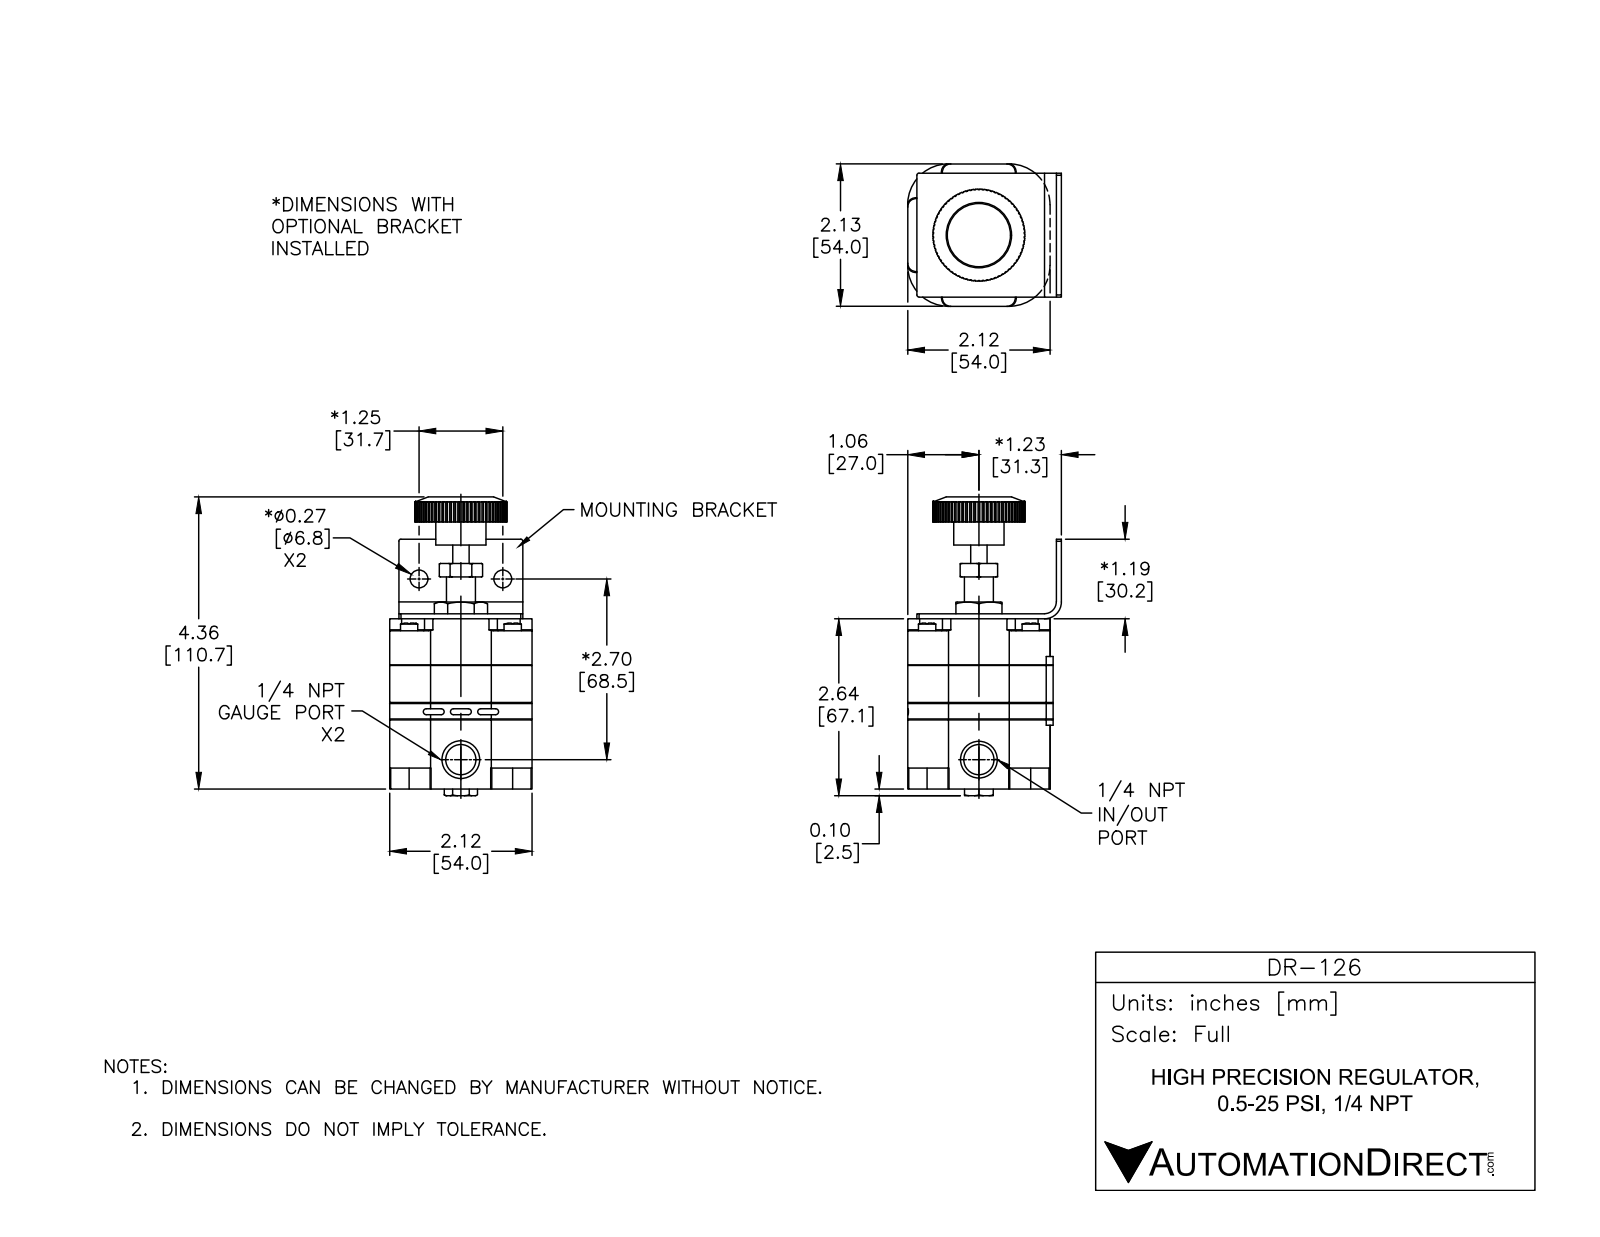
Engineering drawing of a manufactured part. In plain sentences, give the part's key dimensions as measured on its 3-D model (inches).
The part is named "DR-126". Its 3-D file was written by "SolidWorks 2015 (CONFIG_CONTROL_DESIGN)". It is 15 solids with 763 faces: 474 planar, 203 cylindrical and 86 other. Overall it measures 4.46 by 2.171 by 2.125 inches. Its volume is 10.36 cubic inches and its surface area 70.85 square inches. Round holes: 2 of diameter 0.438, 1 of diameter 0.097, 1 of diameter 0.215, 1 of diameter 0.335, 1 of diameter 0.43, 1 of diameter 0.44, 1 of diameter 0.943. Round bosses or shafts: 4 of diameter 0.258, 1 of diameter 0.75, 1 of diameter 0.745, 1 of diameter 0.432, 1 of diameter 0.414, 1 of diameter 0.245. Partial cylindrical surfaces (rounded edges, fillets, slot ends): 20 of radius 0.015, 16 of radius 0.055, 8 of radius 0.125, 6 of radius 0.045, 4 of radius 0.266, 4 of radius 0.313, 4 of radius 0.609, 1 of radius 0.203. The main face-to-face distances are 0.563, 0.26, 0.823, 0.259, 0.822, 0.563, 0.563, 2.125, 1.031, 1.291. The hole center spacings are 0.5, 1.153, 1.163.
